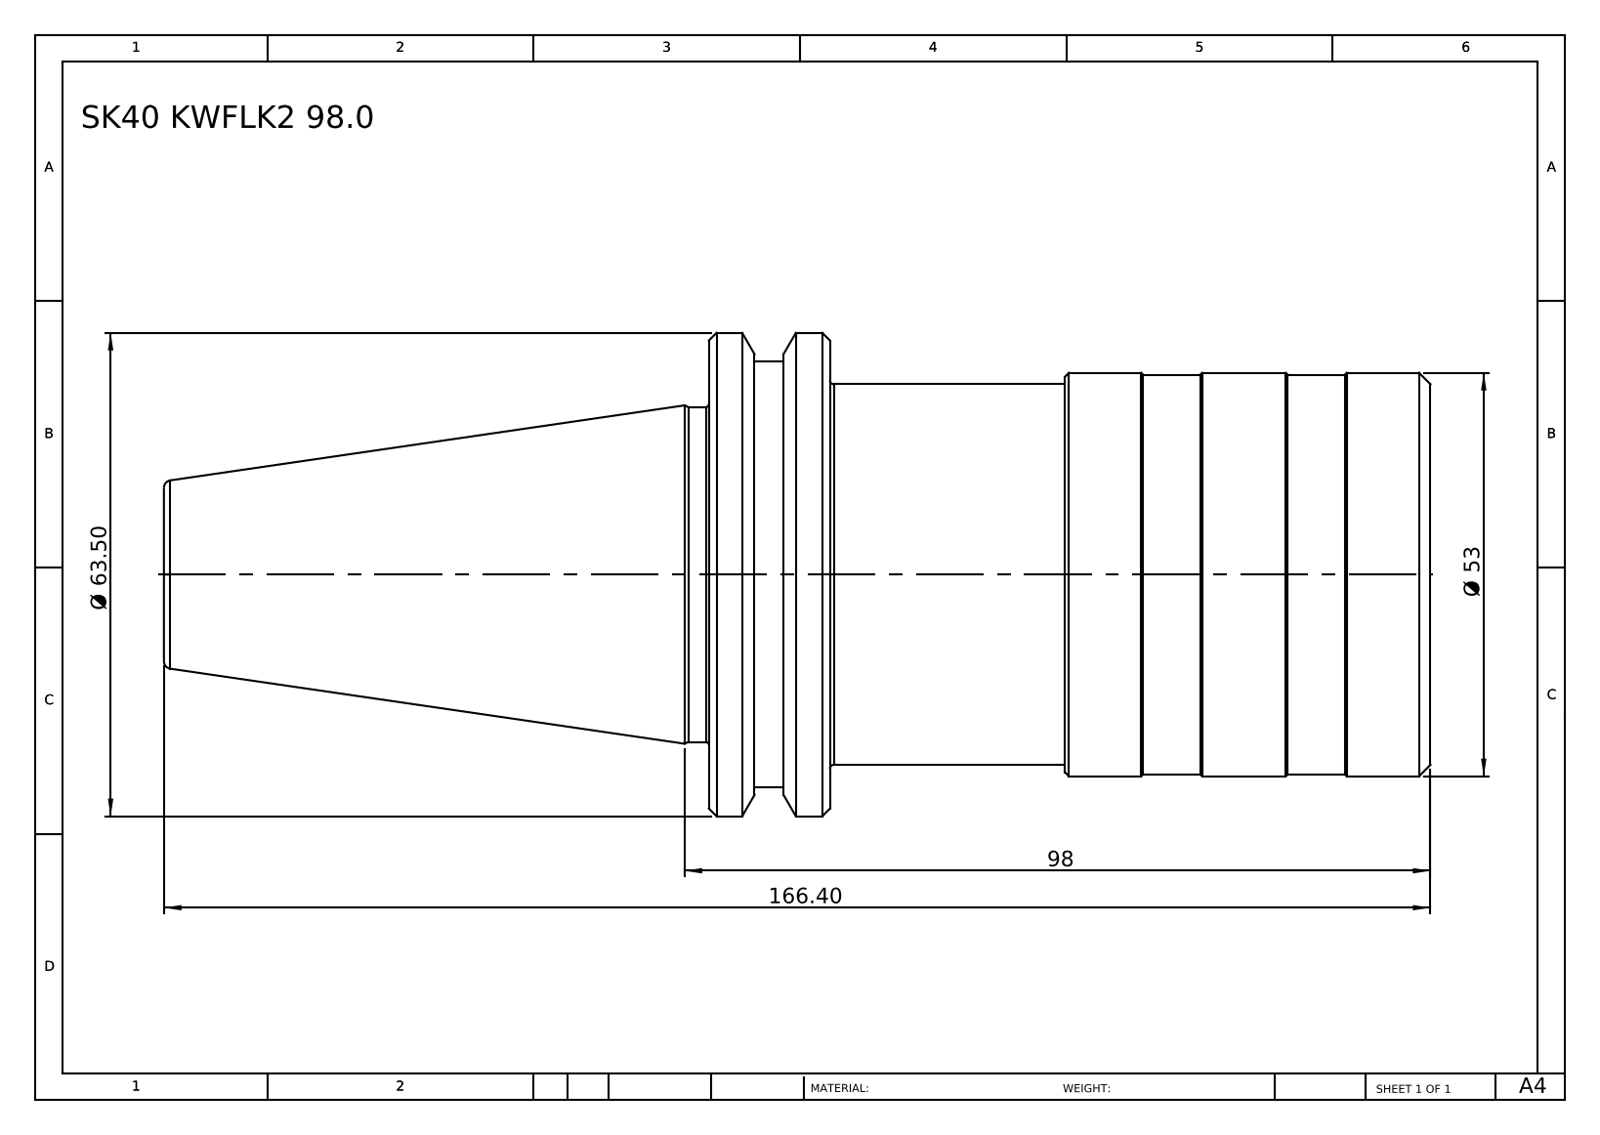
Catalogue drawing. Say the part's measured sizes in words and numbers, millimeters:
The part is named "SK40 KWFLK2 98.0". Its 3-D file was written by "SolidWorks 2014 (CONFIG_CONTROL_DESIGN)". It is 1 solid with 57 faces: 7 planar, 20 cylindrical and 30 other. Overall it measures 166.4 by 63.5 by 63.5 millimeters. Its volume is 282 838 cubic millimeters and its surface area 30 091 square millimeters. Round bosses or shafts: 1 of diameter 63.5, 1 of diameter 56, 1 of diameter 53, 1 of diameter 52.5, 1 of diameter 50, 1 of diameter 44. The main face-to-face distances are 94.8, 78.9, 15.9, 166.4, 87.5, 71.6, 88.8, 9.9, 6, 77.6.
